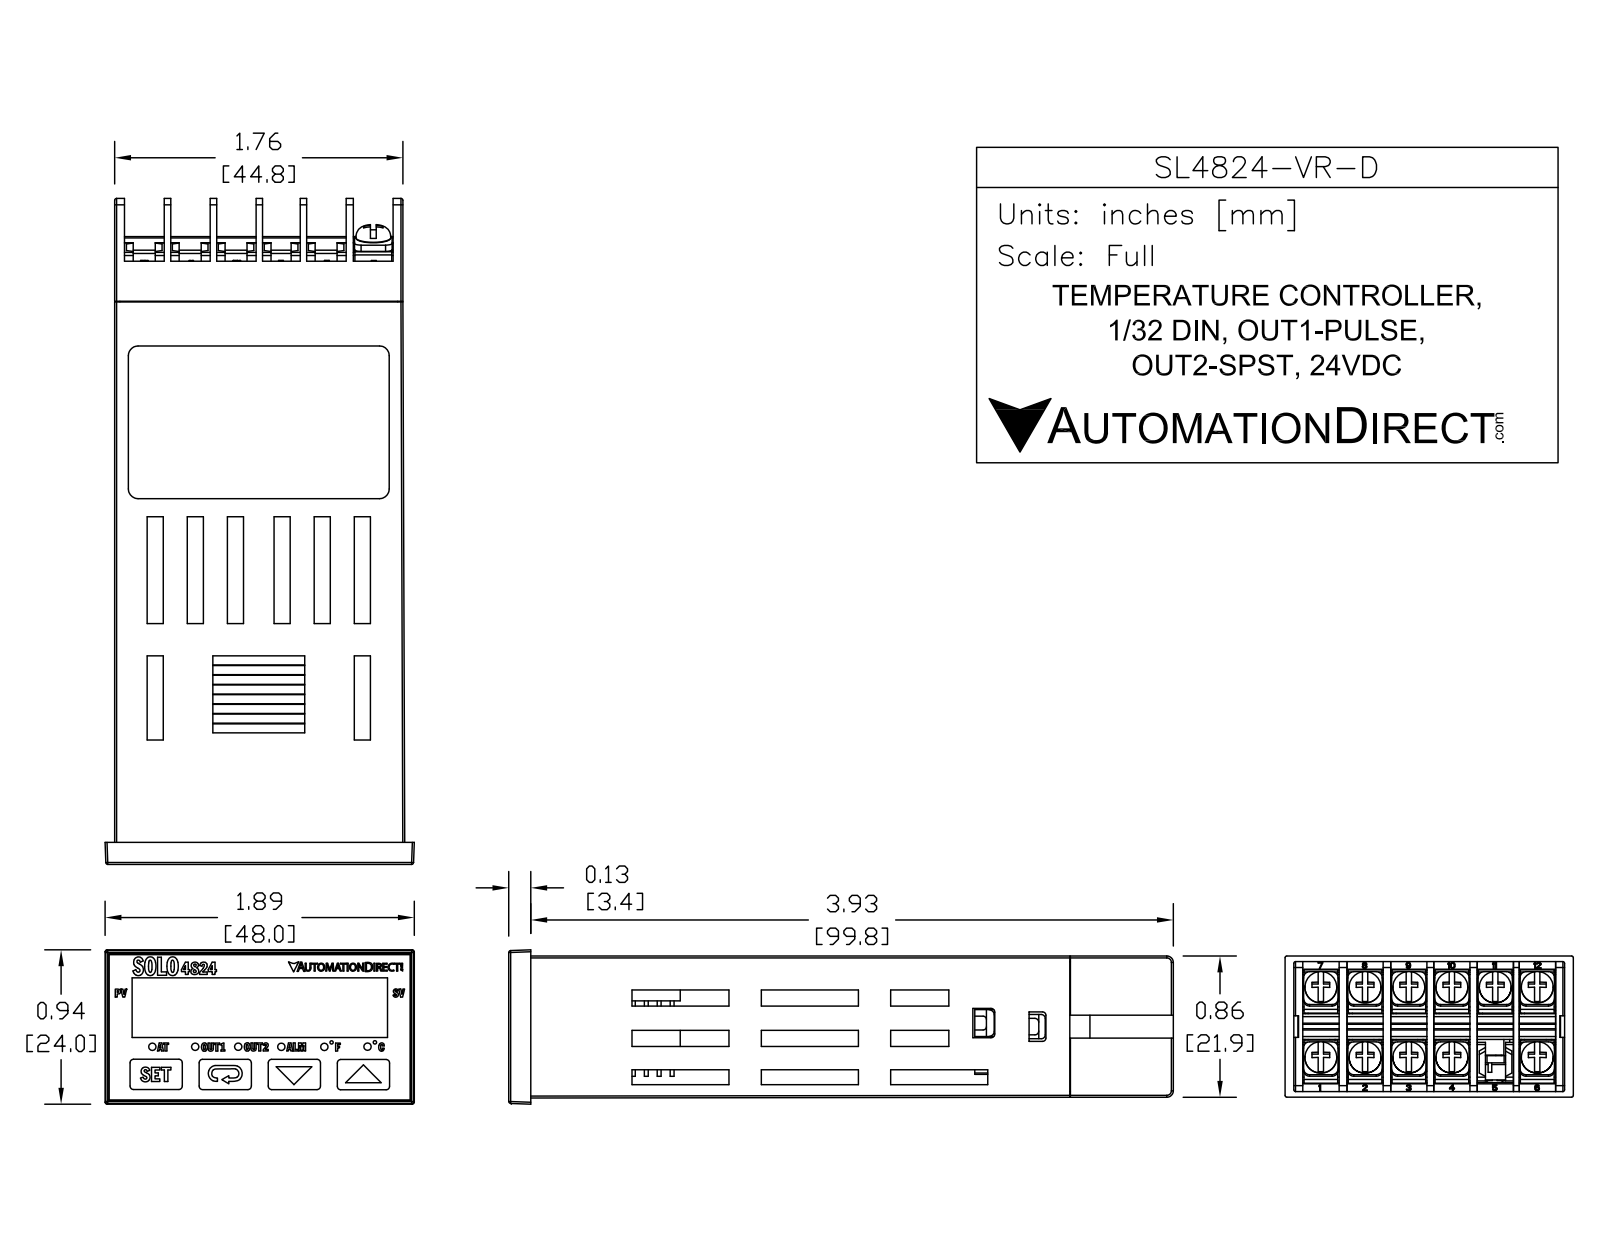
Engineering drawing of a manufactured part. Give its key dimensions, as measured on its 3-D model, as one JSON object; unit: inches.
{"part_name": "SL4824-VR-D", "step_written_by": "SolidWorks 2011 (AUTOMOTIVE_DESIGN)", "units": "inches", "bodies": {"solids": 1, "faces": 992, "planar": 670, "cylindrical": 154, "other": 168}, "overall_size": [4.076, 2.015, 1.125], "volume_in3": 5.814, "surface_area_in2": 31.5, "round_bosses_or_shafts": [[0.185, 12]], "partial_cylinders_radius": [[0.03, 68], [0.015, 14], [0.006, 4], [0.06, 4], [0.025, 2], [0.045, 2]], "face_to_face_distances": [0.86, 0.859, 0.06, 1.76, 0.8, 0.28, 1.7, 0.24, 0.858, 0.84]}
